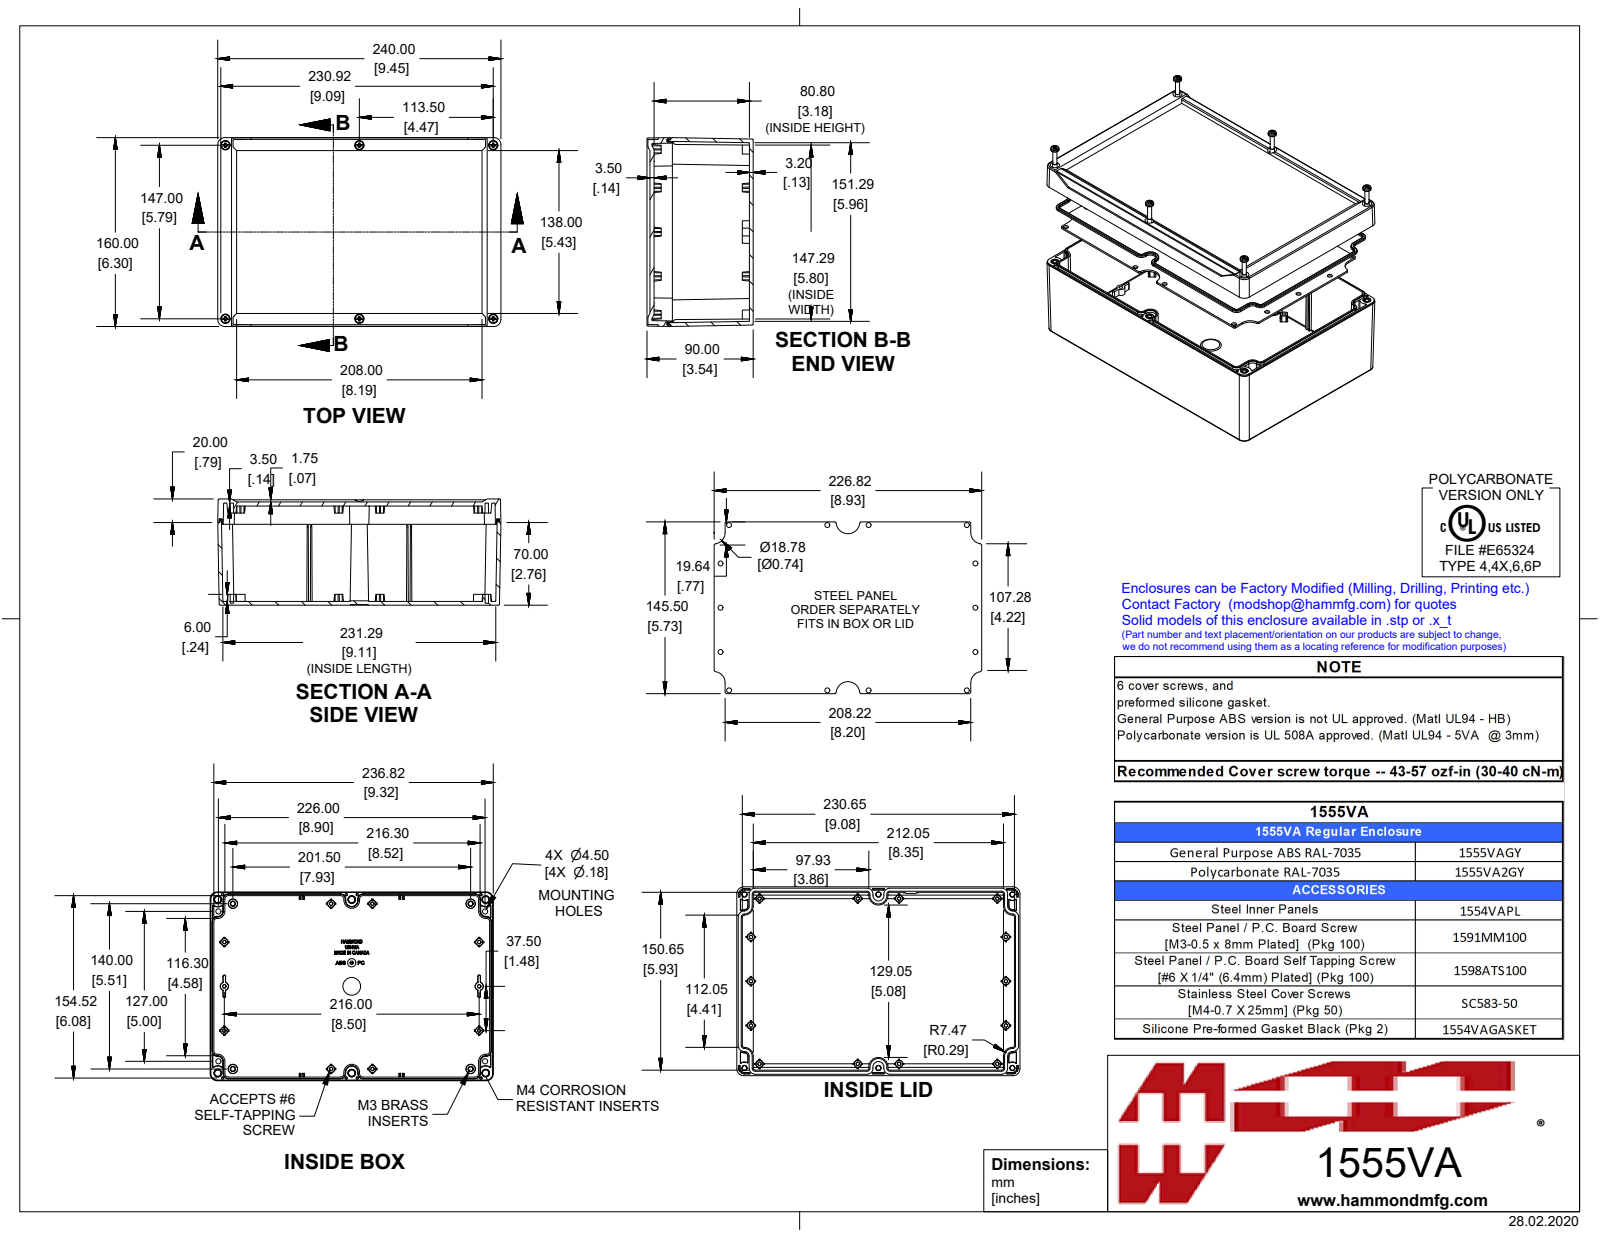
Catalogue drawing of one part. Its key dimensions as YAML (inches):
part_name: "1555VA2GY"
step_written_by: "SolidWorks 2019 (AUTOMOTIVE_DESIGN)"
units: inches
bodies: {solids: 19, faces: 2826, planar: 1285, cylindrical: 483, other: 1058}
overall_size: [9.449, 6.299, 3.543]
volume: 31.15
surface_area: 531.3
round_holes:
  - {diameter: 0.128, count: 6}
  - {diameter: 0.097, count: 4}
  - {diameter: 0.276, count: 1}
  - {diameter: 0.591, count: 1}
round_bosses_or_shafts:
  - {diameter: 0.272, count: 6}
  - {diameter: 0.25, count: 6}
  - {diameter: 0.218, count: 6}
  - {diameter: 0.21, count: 6}
  - {diameter: 0.152, count: 6}
  - {diameter: 0.137, count: 6}
  - {diameter: 0.19, count: 4}
  - {diameter: 0.154, count: 4}
partial_cylinders:
  - {radius: 0.02, count: 55}
  - {radius: 0.012, count: 28}
  - {radius: 0.1, count: 12}
  - {radius: 0.195, count: 12}
  - {radius: 0.039, count: 10}
  - {radius: 0.059, count: 8}
  - {radius: 0.168, count: 8}
  - {radius: 0.236, count: 8}
face_to_face_distances: [0.126, 0.138, 3.181, 3.307, 3.445, 3.319, 0.185, 6.114, 5.988, 9.449]
hole_center_spacings: [0.52, 3.969, 4.469, 4.83, 5.324, 5.672, 6.903, 7.312]
